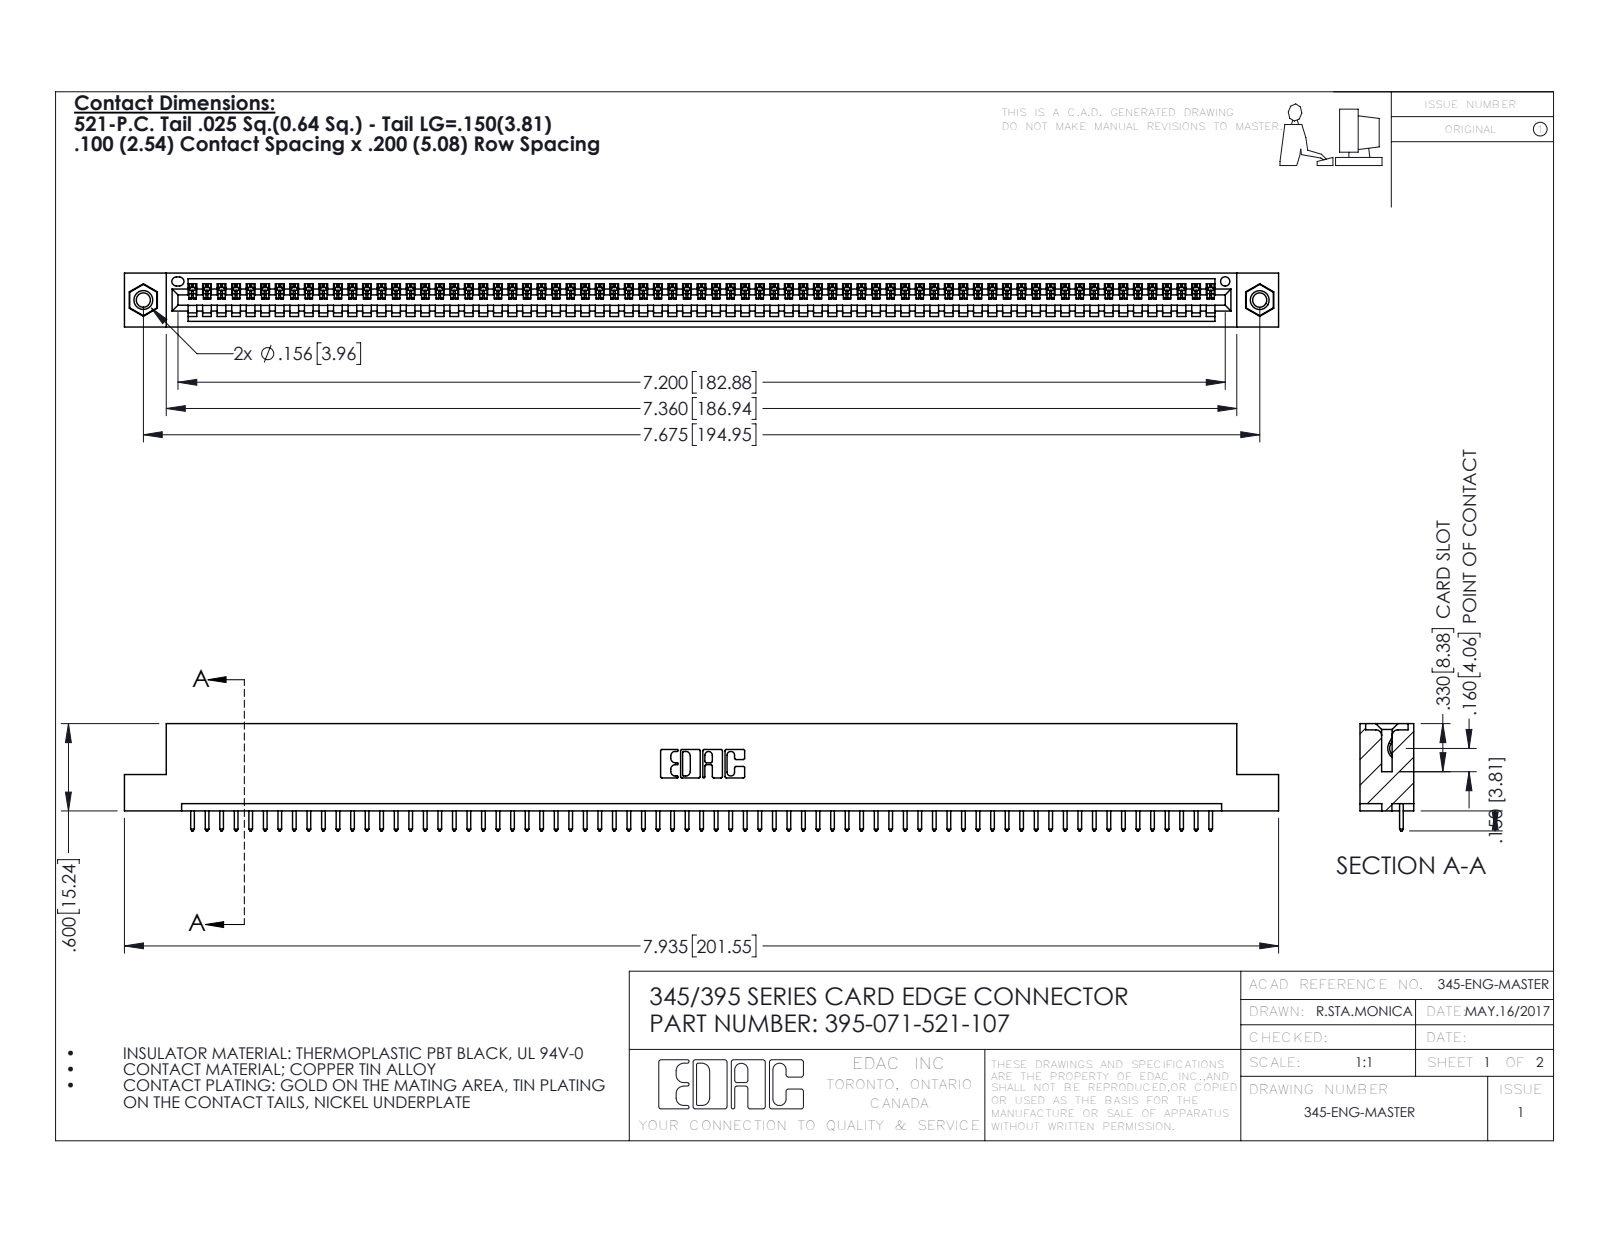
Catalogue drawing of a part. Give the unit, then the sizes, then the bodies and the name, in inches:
Units: inches
Overall size (bounding box): 7.935 × 0.737 × 0.37
Round holes (diameter × count): ⌀0.098 ×2, ⌀0.125 ×2, ⌀0.156 ×2, ⌀0.064 ×1
Round bosses / shafts (diameter × count): ⌀0.155 ×2
Partial cylindrical surfaces — rounded edges, fillets, slot ends (radius × count): R0.006 ×142, R0.01 ×142, R0.01 ×22, R0.007 ×6, R0.031 ×6, R0.026 ×3, R0.031 ×2, R0.04 ×2
Main face-to-face distances: 0.072, 0.298, 0.37, 0.2, 0.098, 0.272, 0.025, 0.225, 0.149, 0.072
Hole centre spacings: 0.27, 7.439, 7.675
Volume: 1.17 in³ · Surface area: 38.91 in²
Bodies: 74 solids, 4304 faces (2952 planar, 1336 cylindrical, 16 other)
Part name (STEP PRODUCT): 345-250-001_345-250-005-103; 345-292-001_345-293-121; 345 Part_Flush Mounting Lugs - 0.156 Dia-TI; 395-071-521-107
STEP written by: SolidWorks 2016 (CONFIG_CONTROL_DESIGN)
